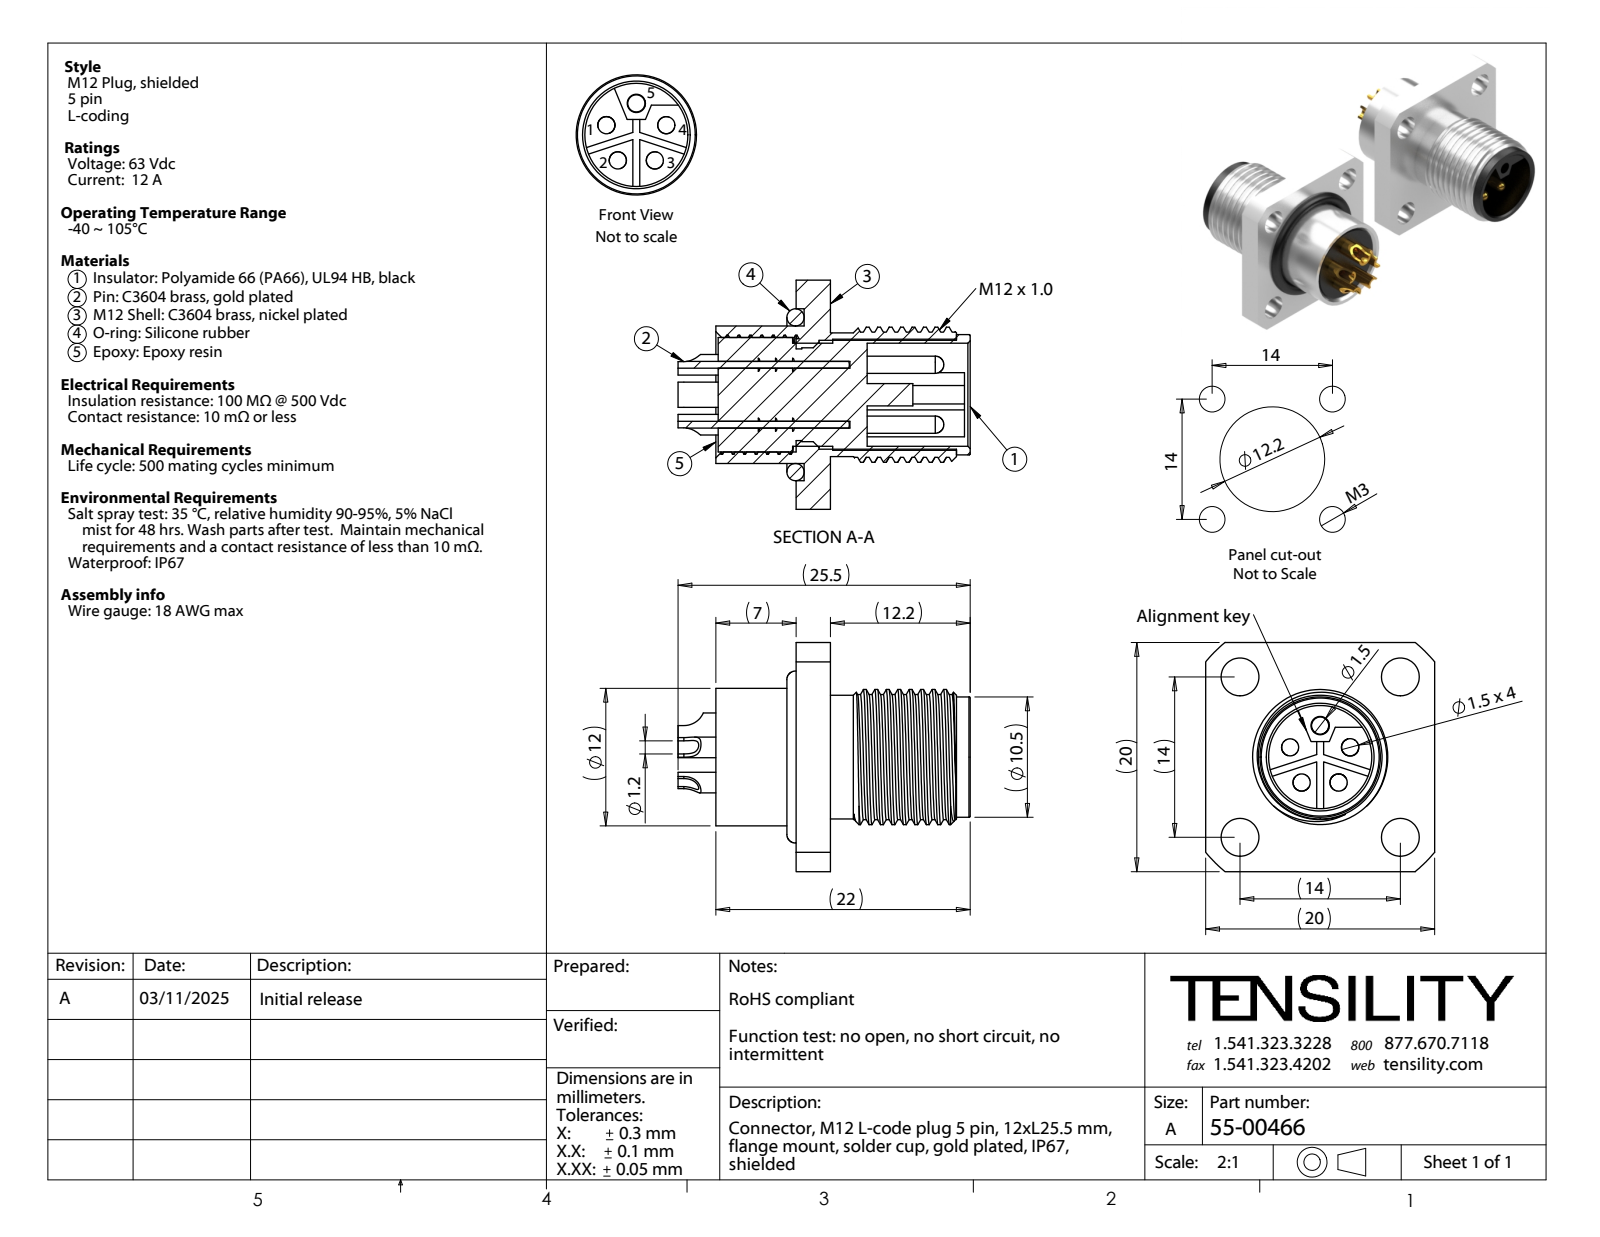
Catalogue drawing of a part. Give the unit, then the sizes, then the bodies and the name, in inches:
Units: inches
Overall size (bounding box): 1.004 × 0.787 × 0.787
Round holes (diameter × count): ⌀0.059 ×5, ⌀0.047 ×4, ⌀0.13 ×4, ⌀0.063 ×1, ⌀0.315 ×1, ⌀0.323 ×1, ⌀0.354 ×1, ⌀0.374 ×1, ⌀0.394 ×1, ⌀0.591 ×1
Round bosses / shafts (diameter × count): ⌀0.071 ×4, ⌀0.472 ×1, ⌀0.465 ×1, ⌀0.43 ×1, ⌀0.425 ×1, ⌀0.413 ×1, ⌀0.382 ×1, ⌀0.087 ×1
Partial cylindrical surfaces — rounded edges, fillets, slot ends (radius × count): R0.067 ×4, R0.073 ×1, R0.512 ×1
Main face-to-face distances: 0.118, 0.787, 0.028, 0.091, 0.295, 0.268, 0.386, 0.024, 0.126, 0.406
Hole centre spacings: 0.108, 0.206, 0.39, 0.551, 0.128, 0.127, 0.283, 0.297
Volume: 0.165 in³ · Surface area: 7.956 in²
Bodies: 8 solids, 334 faces (82 planar, 171 cylindrical, 81 other)
Part name (STEP PRODUCT): 55-00466-04; 55-00466-03; 55-00466-05; 55-00466 (+2 more)
STEP written by: SolidWorks 2021 (CONFIG_CONTROL_DESIGN)
